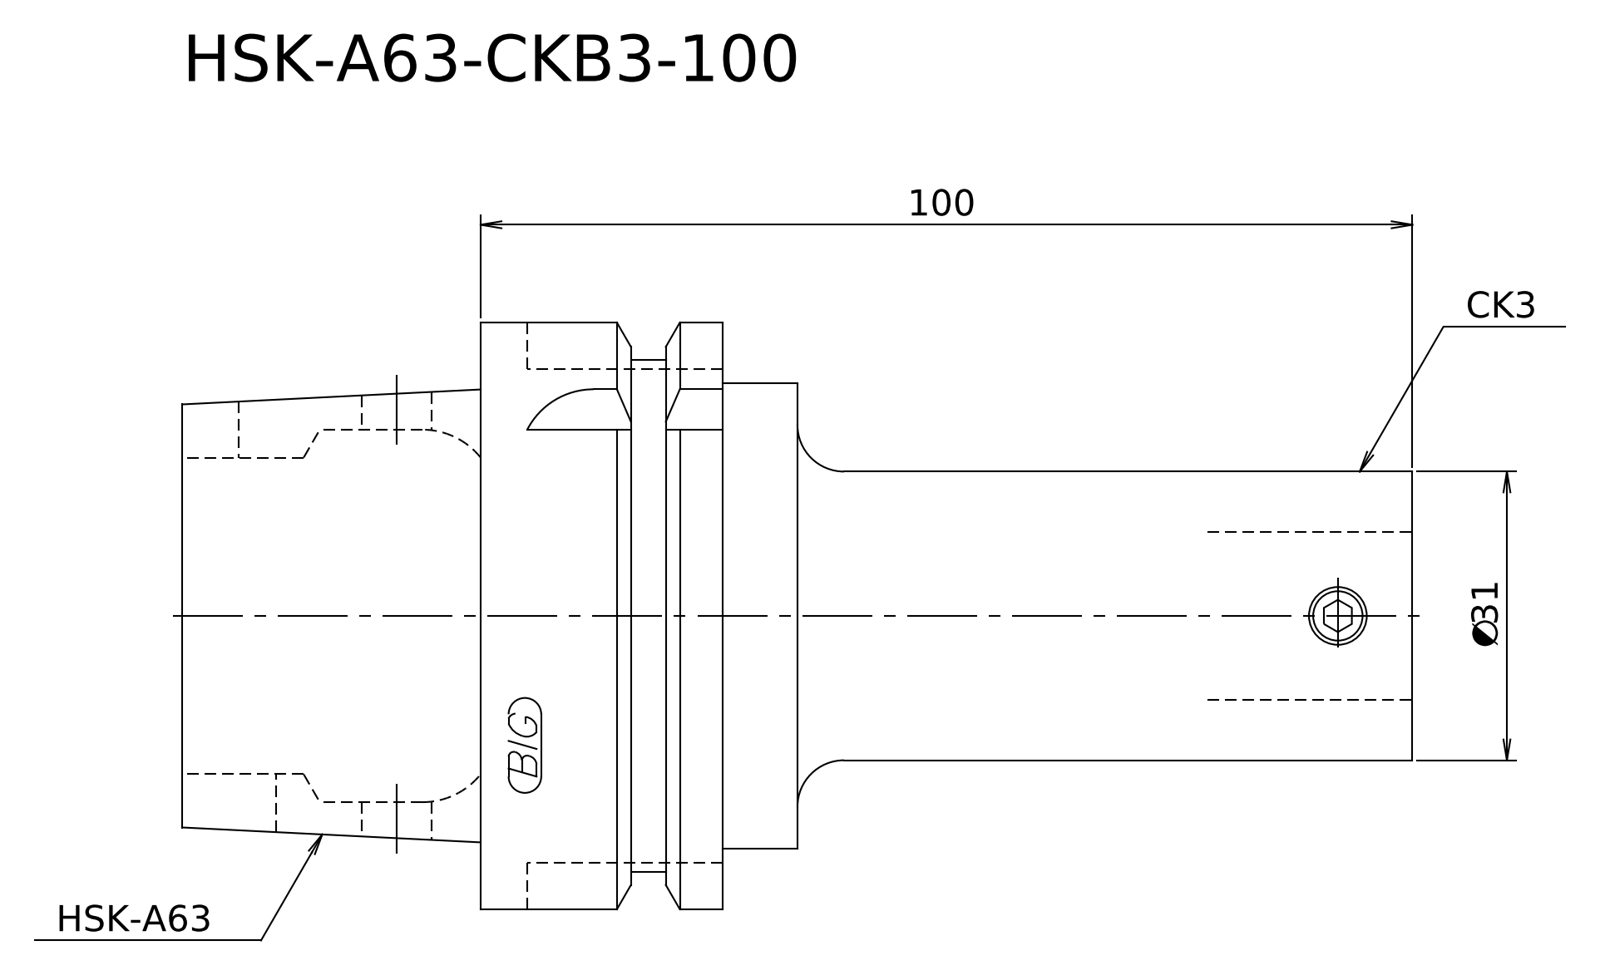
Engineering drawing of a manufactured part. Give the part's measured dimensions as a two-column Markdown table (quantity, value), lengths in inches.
| quantity | value |
| --- | --- |
| STEP written by | Kubotek KeyCreator V8.5.1 (14335) (CONFIG_CONTROL_DESIGN) |
| units | inches |
| bodies | 1 solid, 17 faces (7 planar, 6 cylindrical, 4 other) |
| overall size | 5.197 × 2.48 × 2.48 |
| volume | 12.2 in³ |
| surface area | 37.62 in² |
| round bosses / shafts (diameter × count) | 2.48 × 1, 2.165 × 1, 1.969 × 1, 1.907 × 1, 1.22 × 1 |
| main face-to-face distances | 2.598, 1.26, 1.024, 2.283, 2.913, 3.937, 5.197, 0.315, 1.339, 3.154 |
